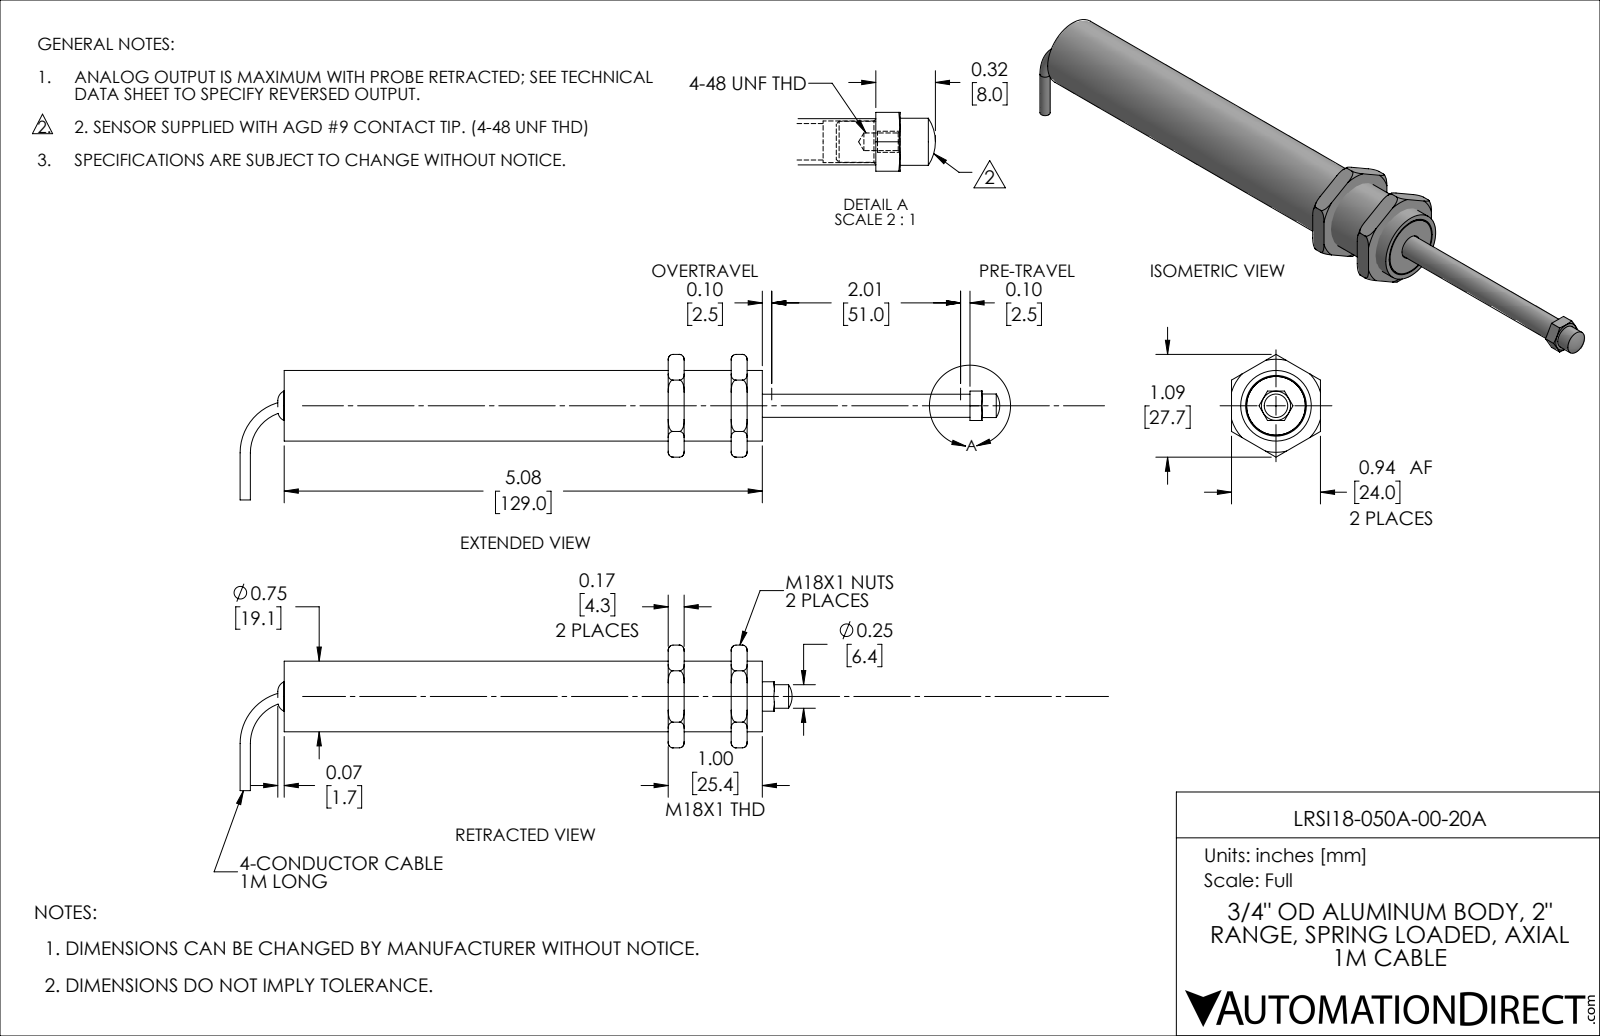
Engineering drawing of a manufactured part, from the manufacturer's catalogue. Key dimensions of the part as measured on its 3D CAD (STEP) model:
Part name (STEP PRODUCT): LRSE18-050A-00-10A_retracted
STEP written by: SolidWorks 2019 (AUTOMOTIVE_DESIGN)
Units: inches
Bodies: 12 solids, 126 faces (52 planar, 29 cylindrical, 45 other)
Overall size (bounding box): 5.865 × 1.546 × 0.945
Volume: 1.126 in³ · Surface area: 34.35 in²
Round holes (diameter × count): ⌀0.093 ×1, ⌀0.109 ×1, ⌀0.188 ×1, ⌀0.261 ×1, ⌀0.307 ×1, ⌀0.5 ×1, ⌀0.566 ×1, ⌀0.62 ×1, ⌀0.625 ×1, ⌀0.65 ×1, ⌀0.665 ×1, ⌀0.71 ×1
Round bosses / shafts (diameter × count): ⌀0.75 ×1, ⌀0.7 ×1, ⌀0.685 ×1, ⌀0.656 ×1, ⌀0.624 ×1, ⌀0.25 ×1, ⌀0.218 ×1, ⌀0.112 ×1
Partial cylindrical surfaces — rounded edges, fillets, slot ends (radius × count): R0.322 ×1
Main face-to-face distances: 0.669, 0.169, 0.945, 4.444, 3.444, 4.113, 1, 0.331, 3.613, 4.283
